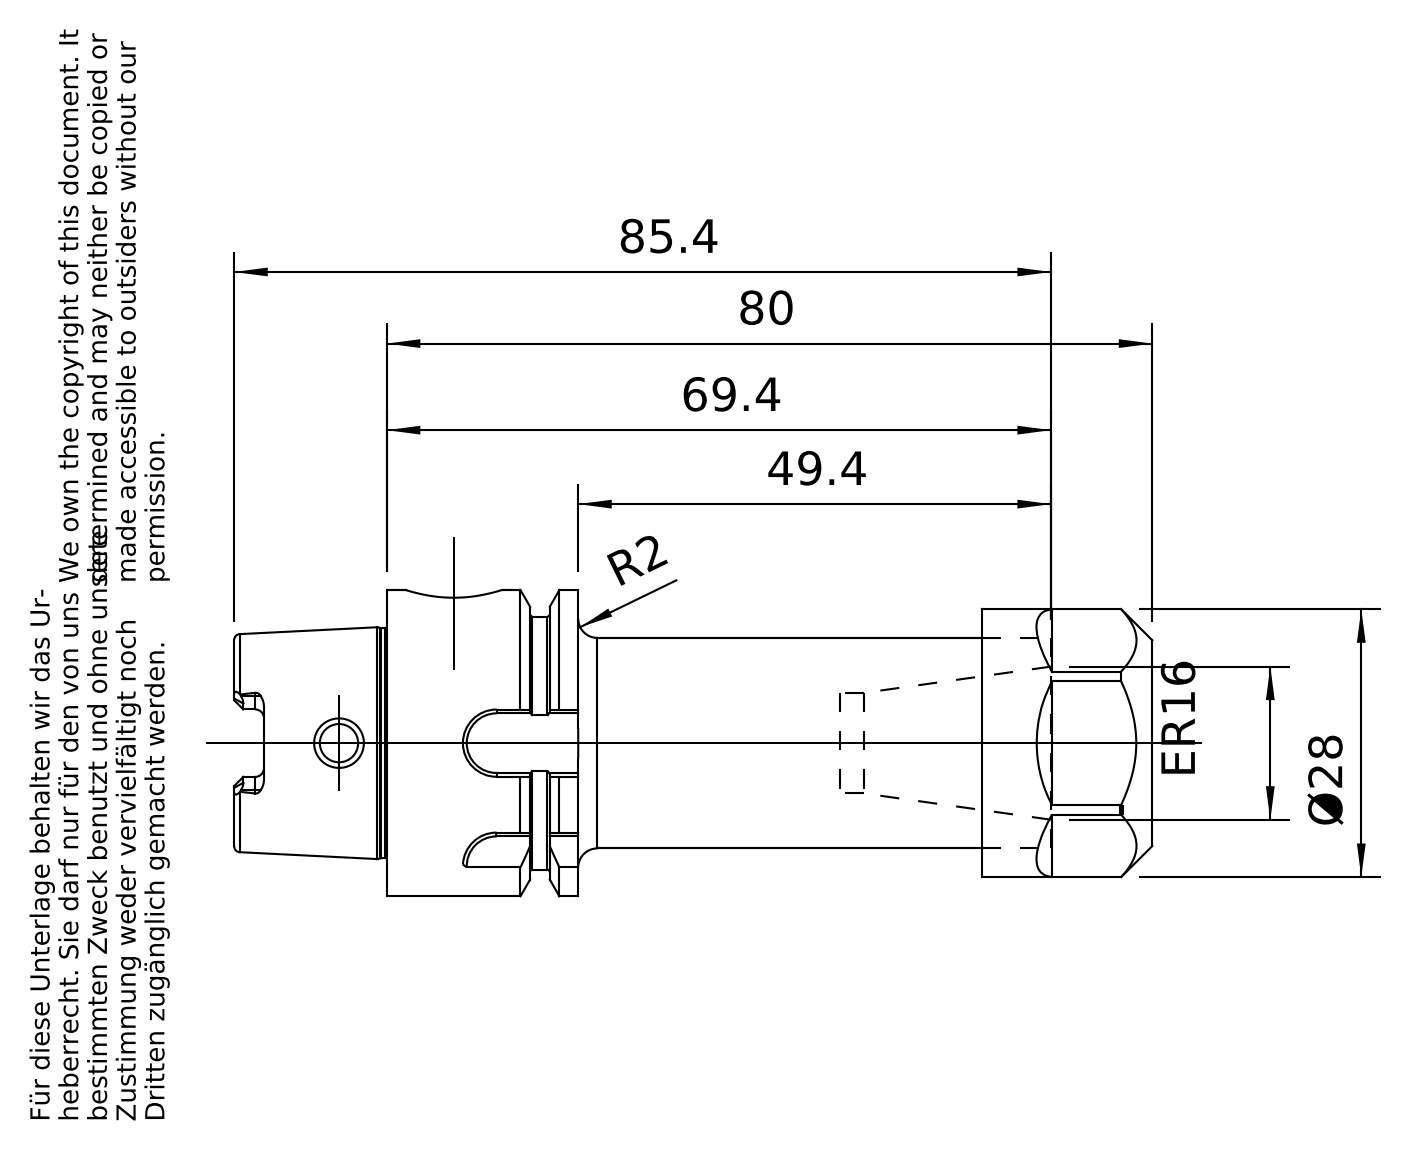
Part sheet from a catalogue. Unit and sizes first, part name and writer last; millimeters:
Units: millimetres
Overall size (bounding box): 95.9 × 32 × 32
Round holes (diameter × count): ⌀10 ×2, ⌀4 ×1, ⌀8.5 ×1, ⌀10.22 ×1, ⌀10.5 ×1, ⌀17.04 ×1, ⌀21.07 ×1
Round bosses / shafts (diameter × count): ⌀32 ×1, ⌀28 ×1, ⌀26.45 ×1, ⌀24.03 ×1, ⌀22 ×1
Partial cylindrical surfaces — rounded edges, fillets, slot ends (radius × count): R0.9 ×6, R1.38 ×4, R3.5 ×3, R3.51 ×1
Main face-to-face distances: 25, 17.8, 62.2, 80, 19.95, 42.25, 60.05, 69.4, 49.45, 7.2
Volume: 40 122 mm³ · Surface area: 13 574 mm²
Bodies: 2 solids, 207 faces (70 planar, 51 cylindrical, 86 other)
Part name (STEP PRODUCT): A32-020-16; 83-912-16; A32-020-16_ASM
STEP written by: PRO/ENGINEER BY PARAMETRIC TECHNOLOGY CORPORATION, 2010430 (CONFIG_CONTROL_DESIGN)
